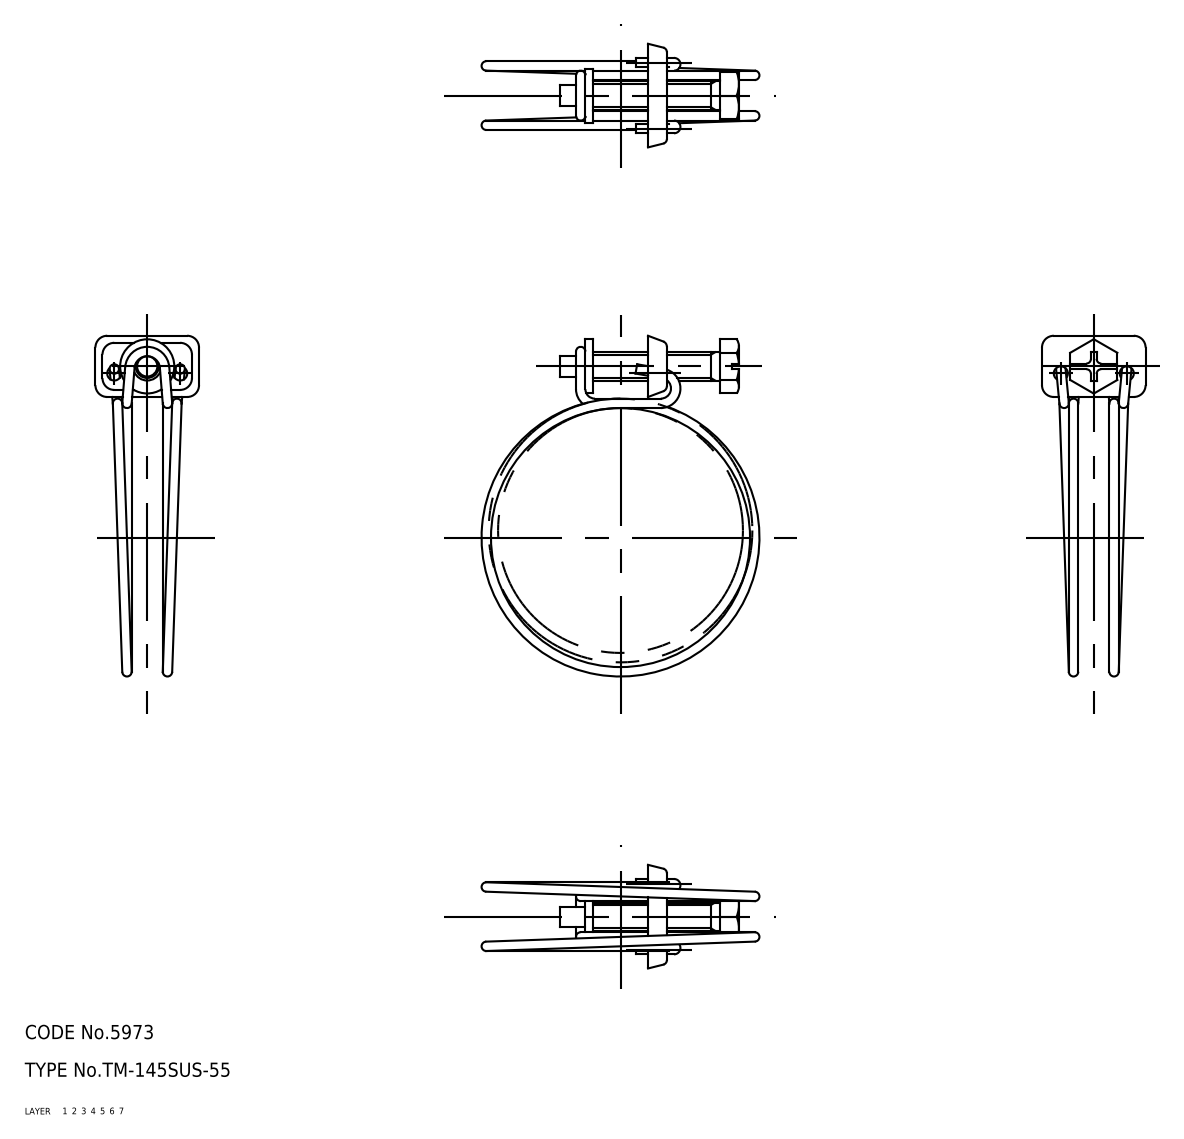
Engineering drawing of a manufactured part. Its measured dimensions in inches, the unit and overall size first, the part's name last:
Units: inches
Overall size (bounding box): 2.848 × 2.323 × 0.866
Volume: 0.197 in³ · Surface area: 7.376 in²
Bodies: 3 solids, 119 faces (0 planar, 0 cylindrical, 119 other)
Part name (STEP PRODUCT): screw; holder; band; TM_145SUS_55_22327_36
STEP written by: CADfix (AUTOMOTIVE_DESIGN)
